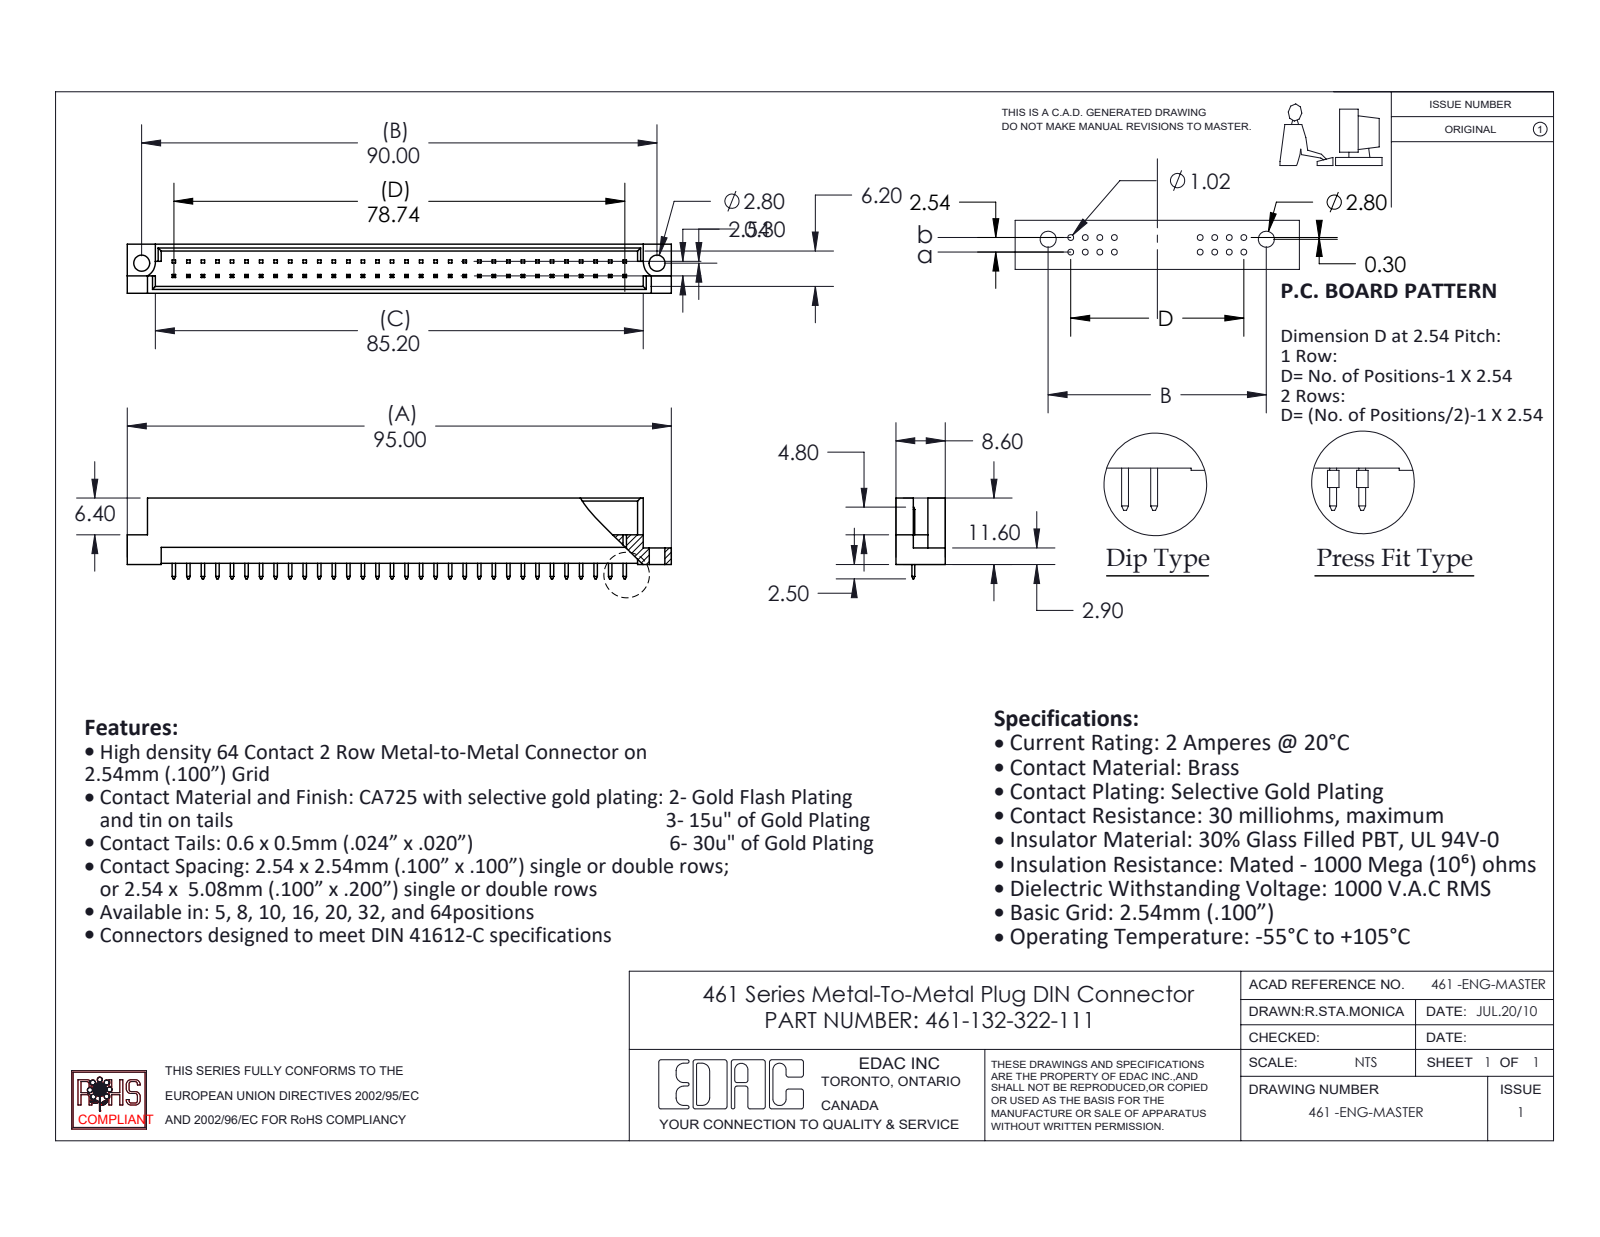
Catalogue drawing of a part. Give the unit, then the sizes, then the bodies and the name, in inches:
Units: inches
Overall size (bounding box): 3.74 × 0.555 × 0.339
Round holes (diameter × count): ⌀0.11 ×2
Partial cylindrical surfaces — rounded edges, fillets, slot ends (radius × count): R0.11 ×2
Main face-to-face distances: 0.047, 0.291, 0.339, 0.244, 0.197, 0.129, 0.209, 0.082, 0.162, 0.109
Hole centre spacings: 3.543
Volume: 0.291 in³ · Surface area: 10.14 in²
Bodies: 33 solids, 753 faces (746 planar, 7 cylindrical, 0 other)
Part name (STEP PRODUCT): 461-132-322-111; 461 Part_64; 461-290_22
STEP written by: SolidWorks 2020 (CONFIG_CONTROL_DESIGN)
